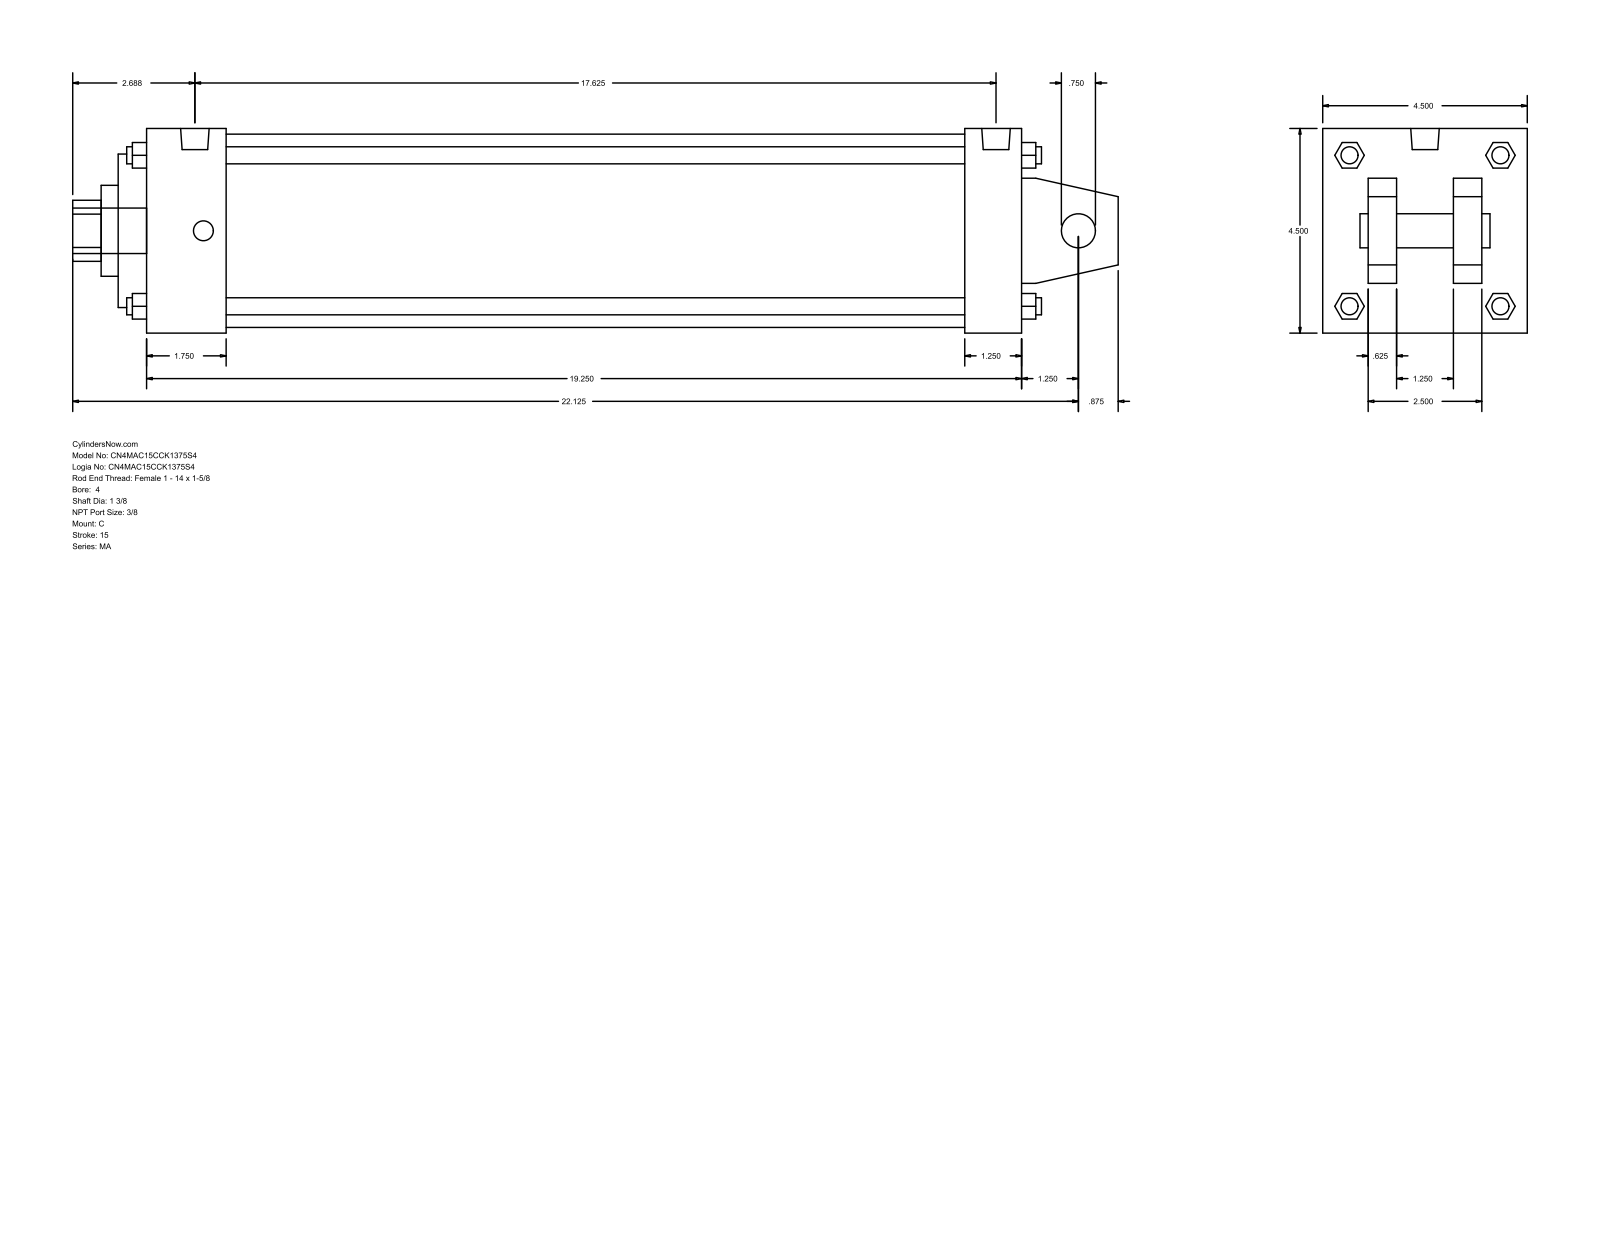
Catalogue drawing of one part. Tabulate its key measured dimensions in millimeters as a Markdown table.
| quantity | value |
| --- | --- |
| part name | MA_C__0400_1.375 |
| STEP written by | GSSL Pune (CONFIG_CONTROL_DESIGN) |
| units | millimeters |
| bodies | 0 solids, 141 faces (109 planar, 32 cylindrical, 0 other) |
| overall size | 584.2 × 114.3 × 114.3 |
| round holes (diameter × count) | 19.05 × 1, 34.92 × 1, 50.8 × 1, 85.72 × 1, 107.95 × 1 |
| round bosses / shafts (diameter × count) | 11.11 × 4, 9.53 × 4, 15.93 × 2, 25.4 × 1 |
| partial cylindrical surfaces (radius × count) | 17.06 × 1 |
| main face-to-face distances | 114.3, 15.87, 488.96, 73.03, 41.27, 25.4, 88.9, 47.63, 504.83, 473.08 |
